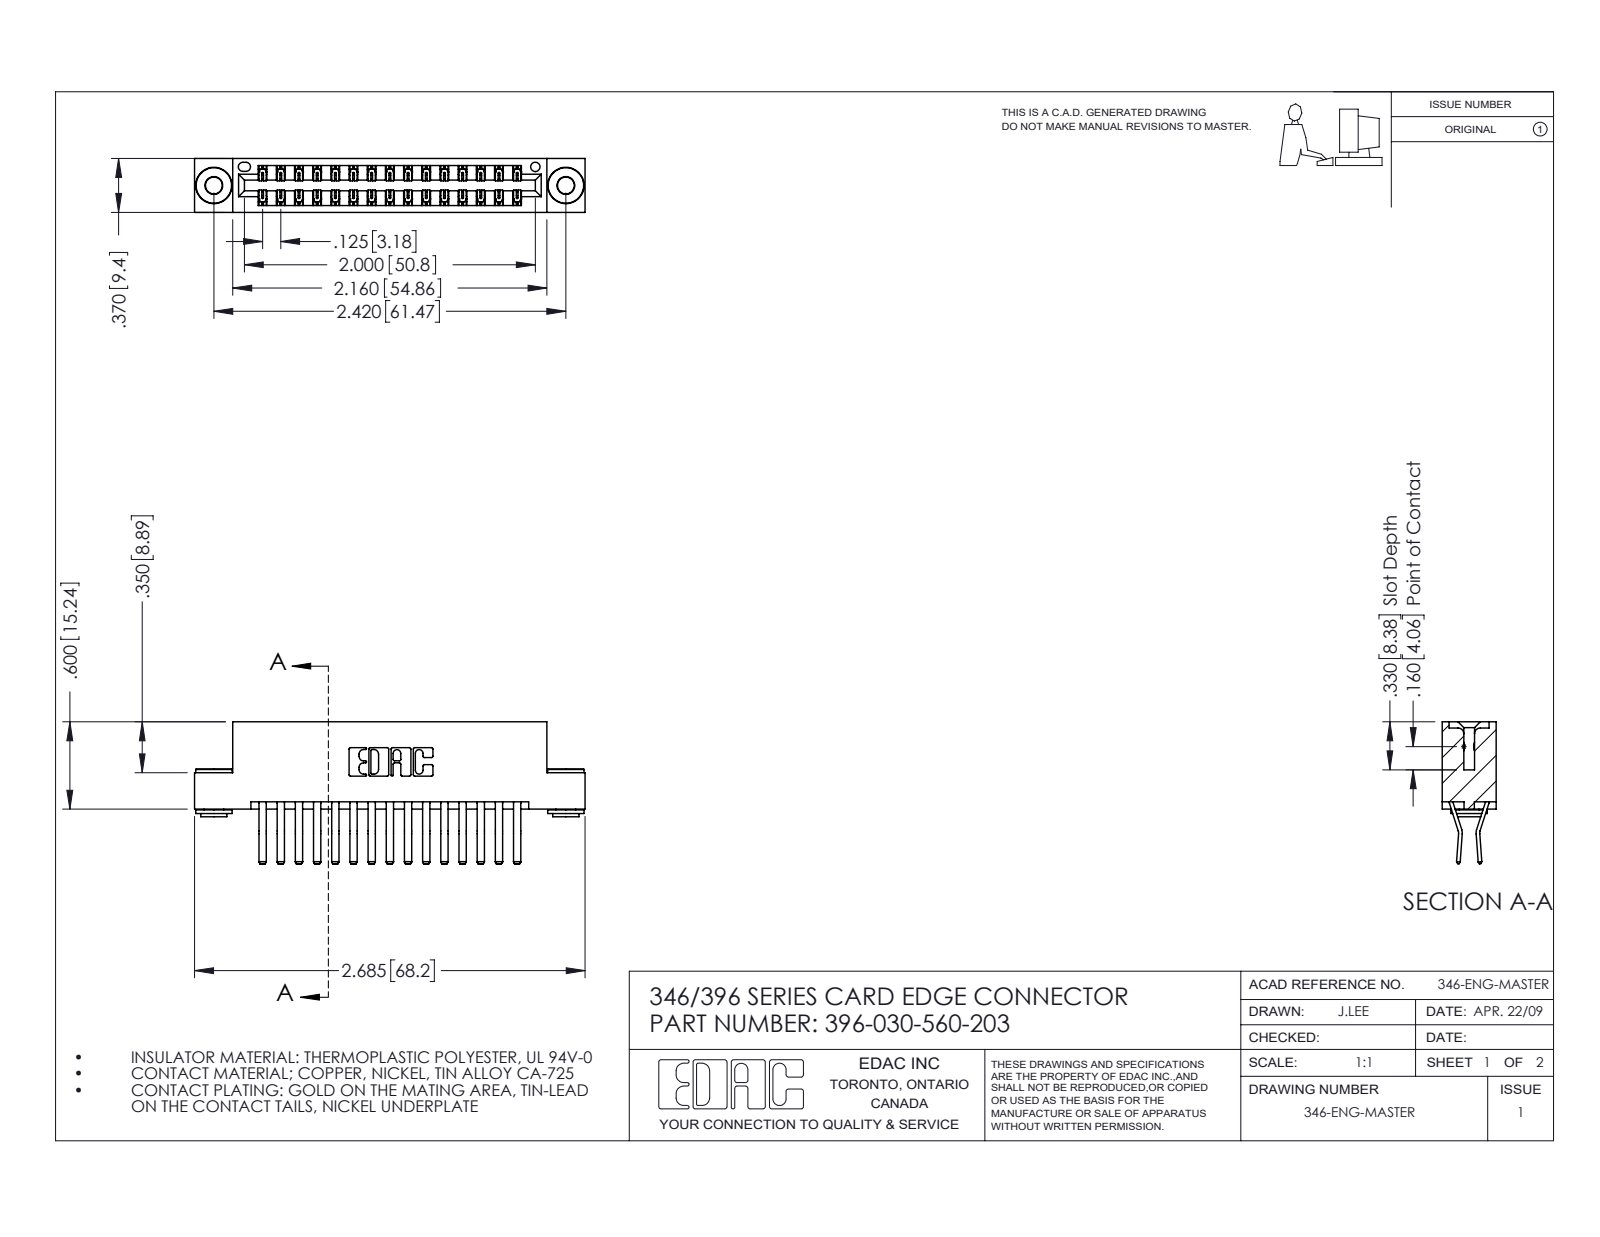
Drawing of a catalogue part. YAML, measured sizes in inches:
part_name: "345-250-002_345-250-002-102; 346 Part_Flush Mounting Lugs - 0.156 Dia-TH; 396-030-560-203; 345-292-001_560 Tail"
step_written_by: "SolidWorks 2016 (CONFIG_CONTROL_DESIGN)"
units: inches
bodies: {solids: 33, faces: 1780, planar: 1136, cylindrical: 636, other: 8}
overall_size: [2.685, 0.975, 0.37]
volume: 0.406
surface_area: 14.67
round_holes:
  - {diameter: 0.116, count: 2}
  - {diameter: 0.156, count: 2}
  - {diameter: 0.064, count: 1}
round_bosses_or_shafts:
  - {diameter: 0.25, count: 2}
  - {diameter: 0.18, count: 2}
  - {diameter: 0.136, count: 2}
partial_cylinders:
  - {radius: 0.006, count: 45}
  - {radius: 0.01, count: 22}
  - {radius: 0.007, count: 6}
  - {radius: 0.031, count: 6}
  - {radius: 0.026, count: 3}
  - {radius: 0.01, count: 2}
  - {radius: 0.014, count: 2}
  - {radius: 0.022, count: 2}
face_to_face_distances: [0.25, 0.048, 0.322, 0.37, 0.025, 0.072, 0.298, 0.275, 0.148, 0.222]
hole_center_spacings: [0.246, 2.213, 2.42]
